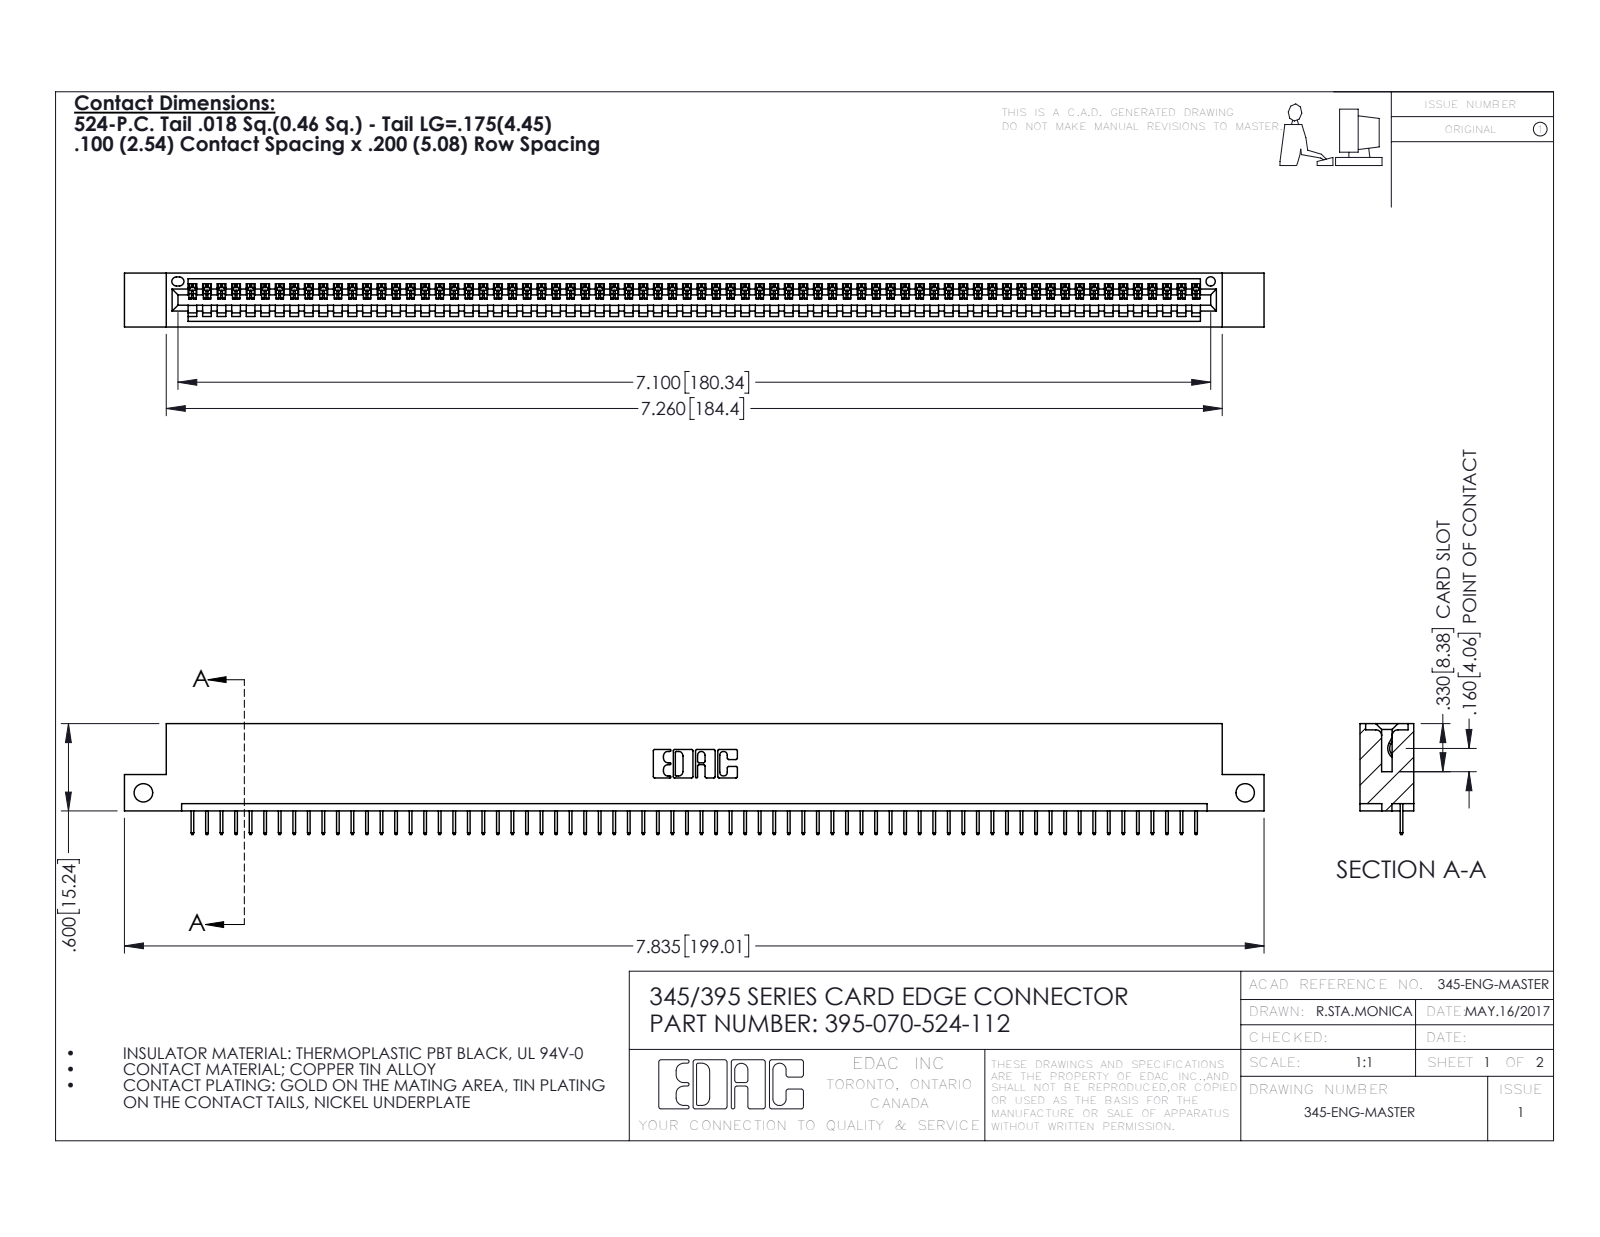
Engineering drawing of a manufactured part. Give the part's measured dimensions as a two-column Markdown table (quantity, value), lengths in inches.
| quantity | value |
| --- | --- |
| part name | 345-292-001_345-293-124; 395-070-524-112; 345 Part_Flush Mounting Lugs - Side Mount |
| STEP written by | SolidWorks 2016 (CONFIG_CONTROL_DESIGN) |
| units | inches |
| bodies | 71 solids, 4466 faces (3300 planar, 1166 cylindrical, 0 other) |
| overall size | 7.835 × 0.762 × 0.37 |
| volume | 1.145 in³ |
| surface area | 37.66 in² |
| round holes (diameter × count) | 0.128 × 2, 0.064 × 1 |
| partial cylindrical surfaces (radius × count) | 0.006 × 140, 0.01 × 22, 0.007 × 6, 0.031 × 6, 0.026 × 3, 0.031 × 2, 0.04 × 2, 0.014 × 1 |
| main face-to-face distances | 0.298, 0.072, 0.37, 0.2, 0.098, 0.272, 0.025, 0.225, 0.072, 0.149 |
| hole center spacings | 7.575 |
